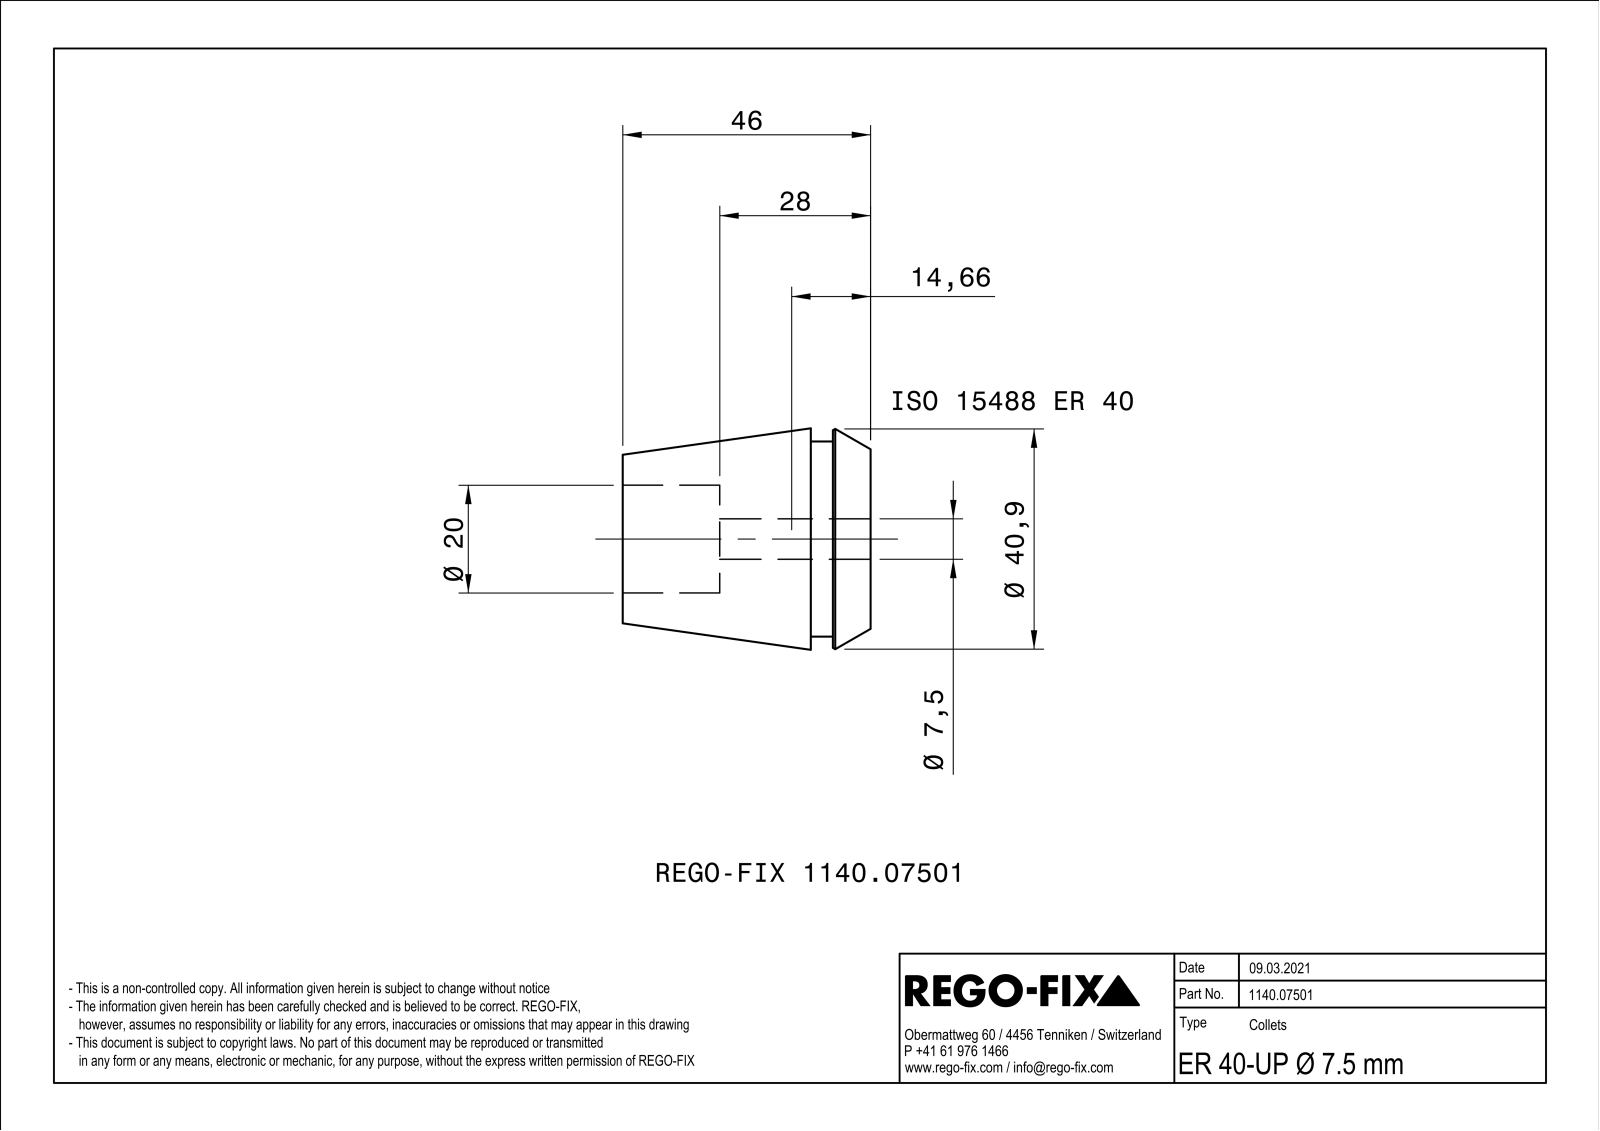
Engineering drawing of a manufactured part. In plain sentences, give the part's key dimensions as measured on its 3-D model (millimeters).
The part is named "NOCUT". Its 3-D file was written by "SIEMENS PLM Software Solid Edge ST10 (AUTOMOTIVE_DESIGN)". It is 1 solid with 272 faces: 104 planar, 48 cylindrical and 120 other. Overall it measures 46 by 40.99 by 40.99 millimeters. Its volume is 35 784 cubic millimeters and its surface area 21 132 square millimeters. Round holes: 1 of diameter 20. Round bosses or shafts: 1 of diameter 36.2. Partial cylindrical surfaces (rounded edges, fillets, slot ends): 8 of radius 45, 1 of radius 3.75. The main face-to-face distances are 0.8, 0.78, 0.82, 46, 11.1, 34.9, 7, 4.1, 39, 28.
